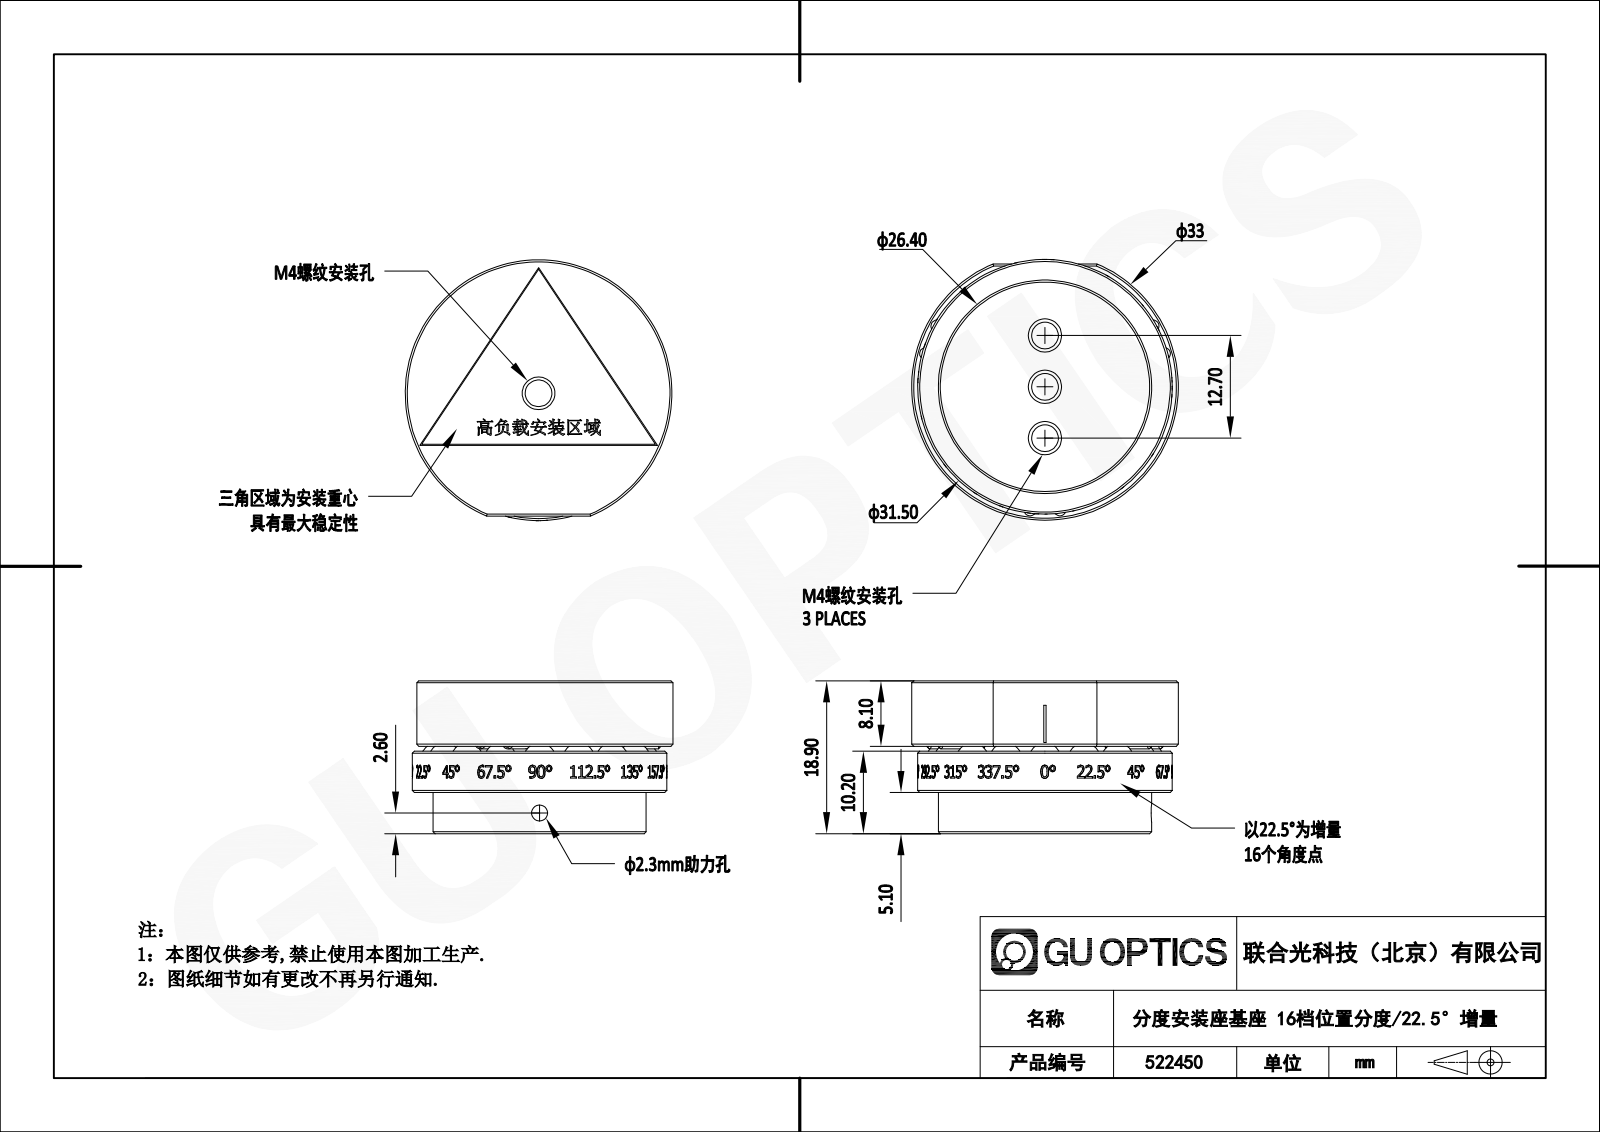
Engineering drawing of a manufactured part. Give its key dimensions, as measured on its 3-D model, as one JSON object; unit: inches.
{"part_name": "1.3.7.1_ZZF-16NX_完整16档位螺纹分度安装座基座，M4螺孔", "step_written_by": "SolidWorks 2021 (CONFIG_CONTROL_DESIGN)", "units": "inches", "bodies": {"solids": 0, "faces": 704, "planar": 203, "cylindrical": 140, "other": 361}, "overall_size": [1.299, 1.27, 0.744], "round_holes": [[0.13, 3], [0.091, 1]], "round_bosses_or_shafts": [[0.059, 6], [1.299, 1], [1.24, 1], [1.039, 1]], "partial_cylinders_radius": [[0.03, 6], [0.619, 1]], "face_to_face_distances": [0.744, 0.201, 0.402, 0.343, 0.543, 0.024, 0.425, 0.224, 0.319, 0.059], "hole_center_spacings": [0.25, 0.5]}
